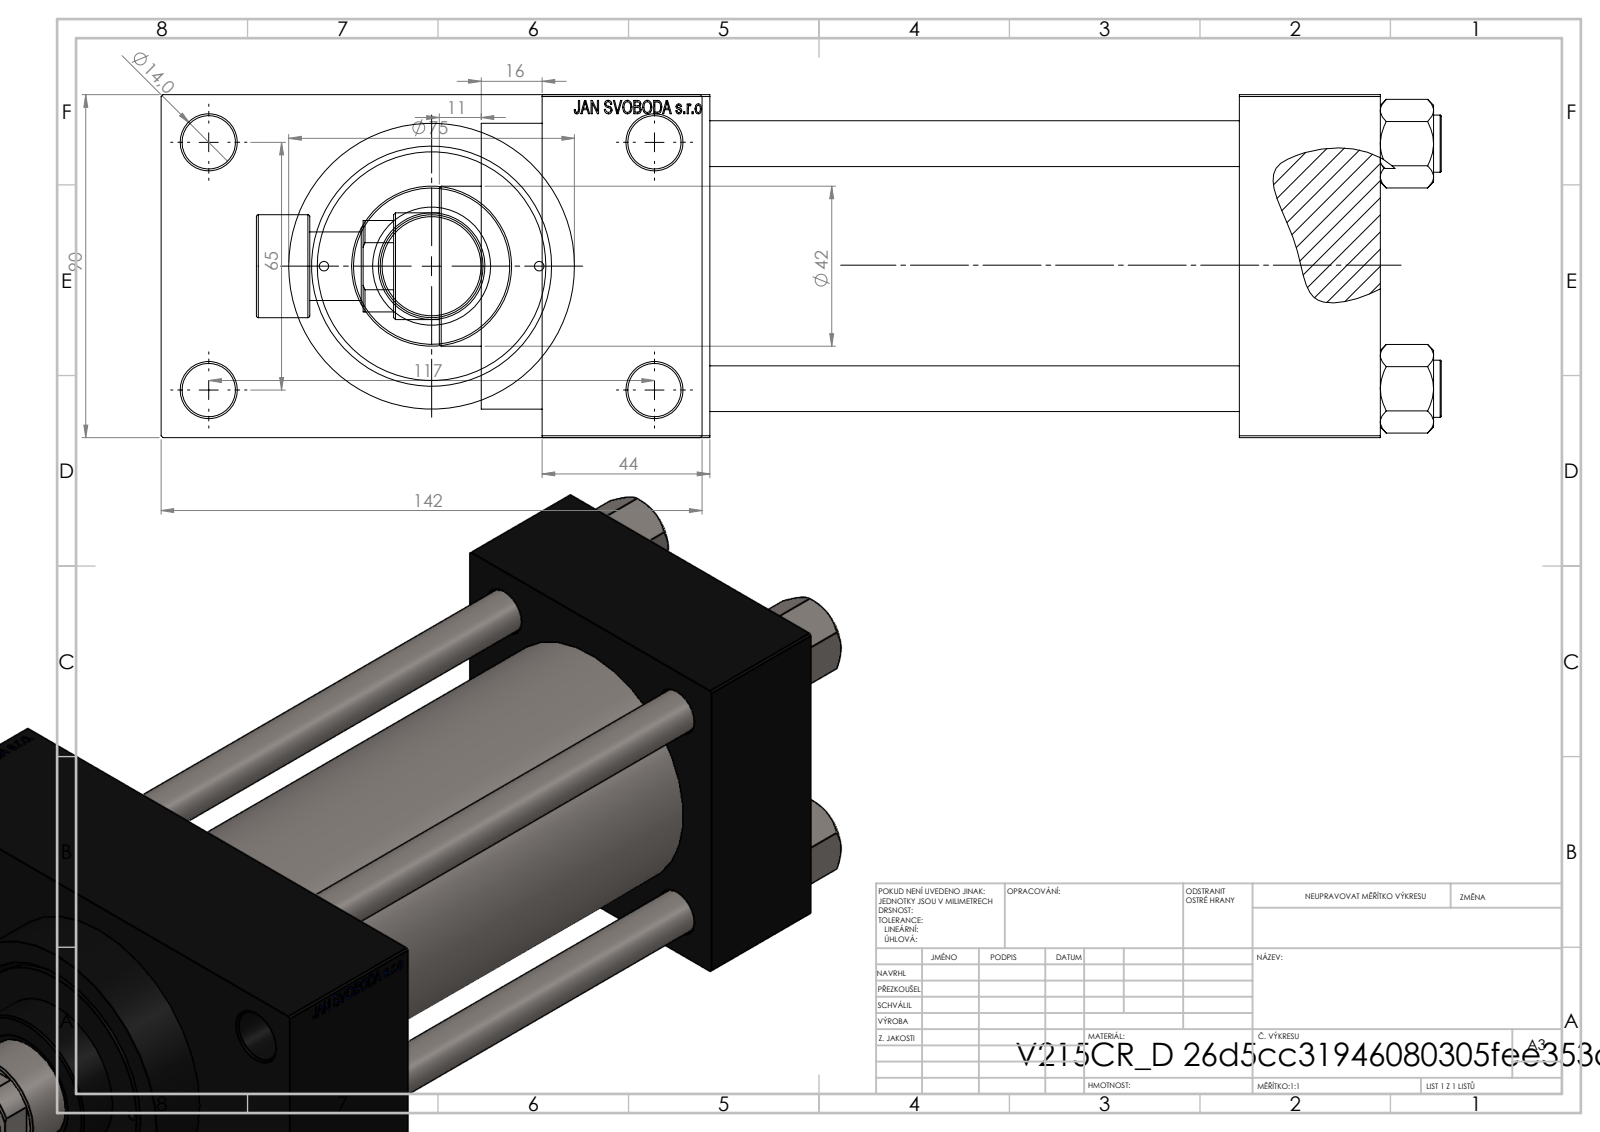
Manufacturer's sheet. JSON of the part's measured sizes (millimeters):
{"part_name": "V215CR_D_Body; V215CR_D_TYCINKA; V215CR_ROD_END_F; NUT_M5_D (+2 more)", "step_written_by": "SolidWorks 2019 (CONFIG_CONTROL_DESIGN)", "units": "millimeters", "bodies": {"solids": 12, "faces": 1125, "planar": 503, "cylindrical": 96, "other": 526}, "overall_size": [311, 142, 90], "volume_mm3": 1243000, "surface_area_mm2": 255762, "round_holes": [[12, 4], [14, 4], [2.5, 2], [7, 2], [20.96, 2], [30, 2], [18.5, 1], [28, 1], [31, 1], [50, 1], [60, 1], [63, 1]], "round_bosses_or_shafts": [[15, 4], [75, 1], [69, 1], [42, 1], [27, 1], [18, 1]], "face_to_face_distances": [90, 139, 37, 176, 183, 220, 44, 26, 116, 16], "hole_center_spacings": [26.35, 32.39, 44.4, 45.47, 64.3, 66.92, 68.42, 69.81]}
